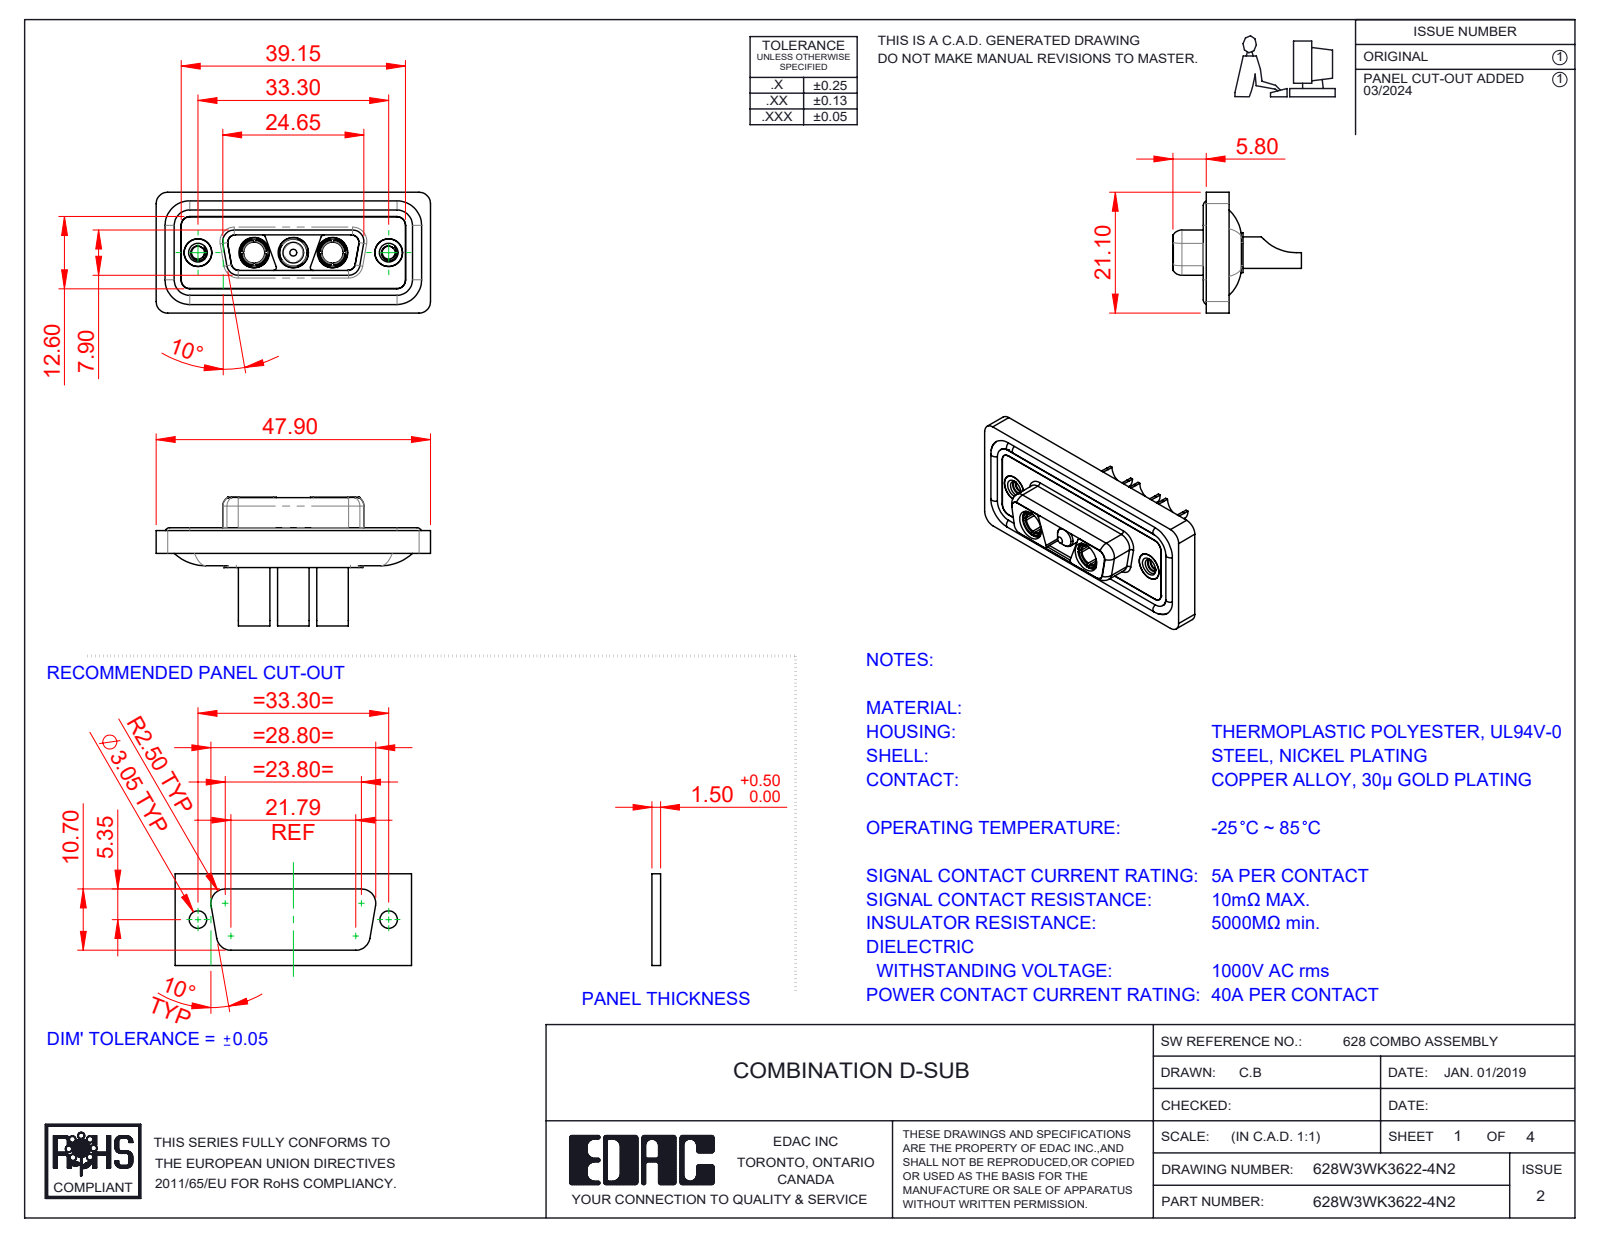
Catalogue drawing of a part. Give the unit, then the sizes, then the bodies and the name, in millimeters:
Units: millimetres
Overall size (bounding box): 47.9 × 22.45 × 21.1
Round holes (diameter × count): ⌀4.85 ×5, ⌀4.6 ×3, ⌀5.3 ×3, ⌀2.26 ×2, ⌀3.7 ×2, ⌀4 ×2, ⌀4.05 ×2, ⌀5 ×2
Round bosses / shafts (diameter × count): ⌀1.6 ×4, ⌀5.5 ×3, ⌀5.2 ×3, ⌀4.75 ×3, ⌀3.75 ×3, ⌀4.96 ×2, ⌀4.95 ×2, ⌀4.8 ×2
Partial cylindrical surfaces — rounded edges, fillets, slot ends (radius × count): R1.5 ×22, R2 ×20, R1.35 ×12, R0.5 ×8, R1.6 ×8, R0.25 ×4, R0.6 ×4, R0.65 ×4
Main face-to-face distances: 0.4, 1.6, 0.5, 1.1, 2.9, 5.65, 1.8, 7.05, 5.35, 6.6
Hole centre spacings: 6.85, 9.8, 16.65, 23.5, 13.7, 33.3
Volume: 5 998 mm³ · Surface area: 9 924 mm²
Bodies: 13 solids, 593 faces (184 planar, 261 cylindrical, 148 other)
Part name (STEP PRODUCT): 628Combo Threaded Rivet_2; 628Combo Shell Front_15 Contacts; 628W3WK3622-4N2; 628Combo Waterproof Housing_15 Contacts (+4 more)
STEP written by: SolidWorks 2023 (CONFIG_CONTROL_DESIGN)
